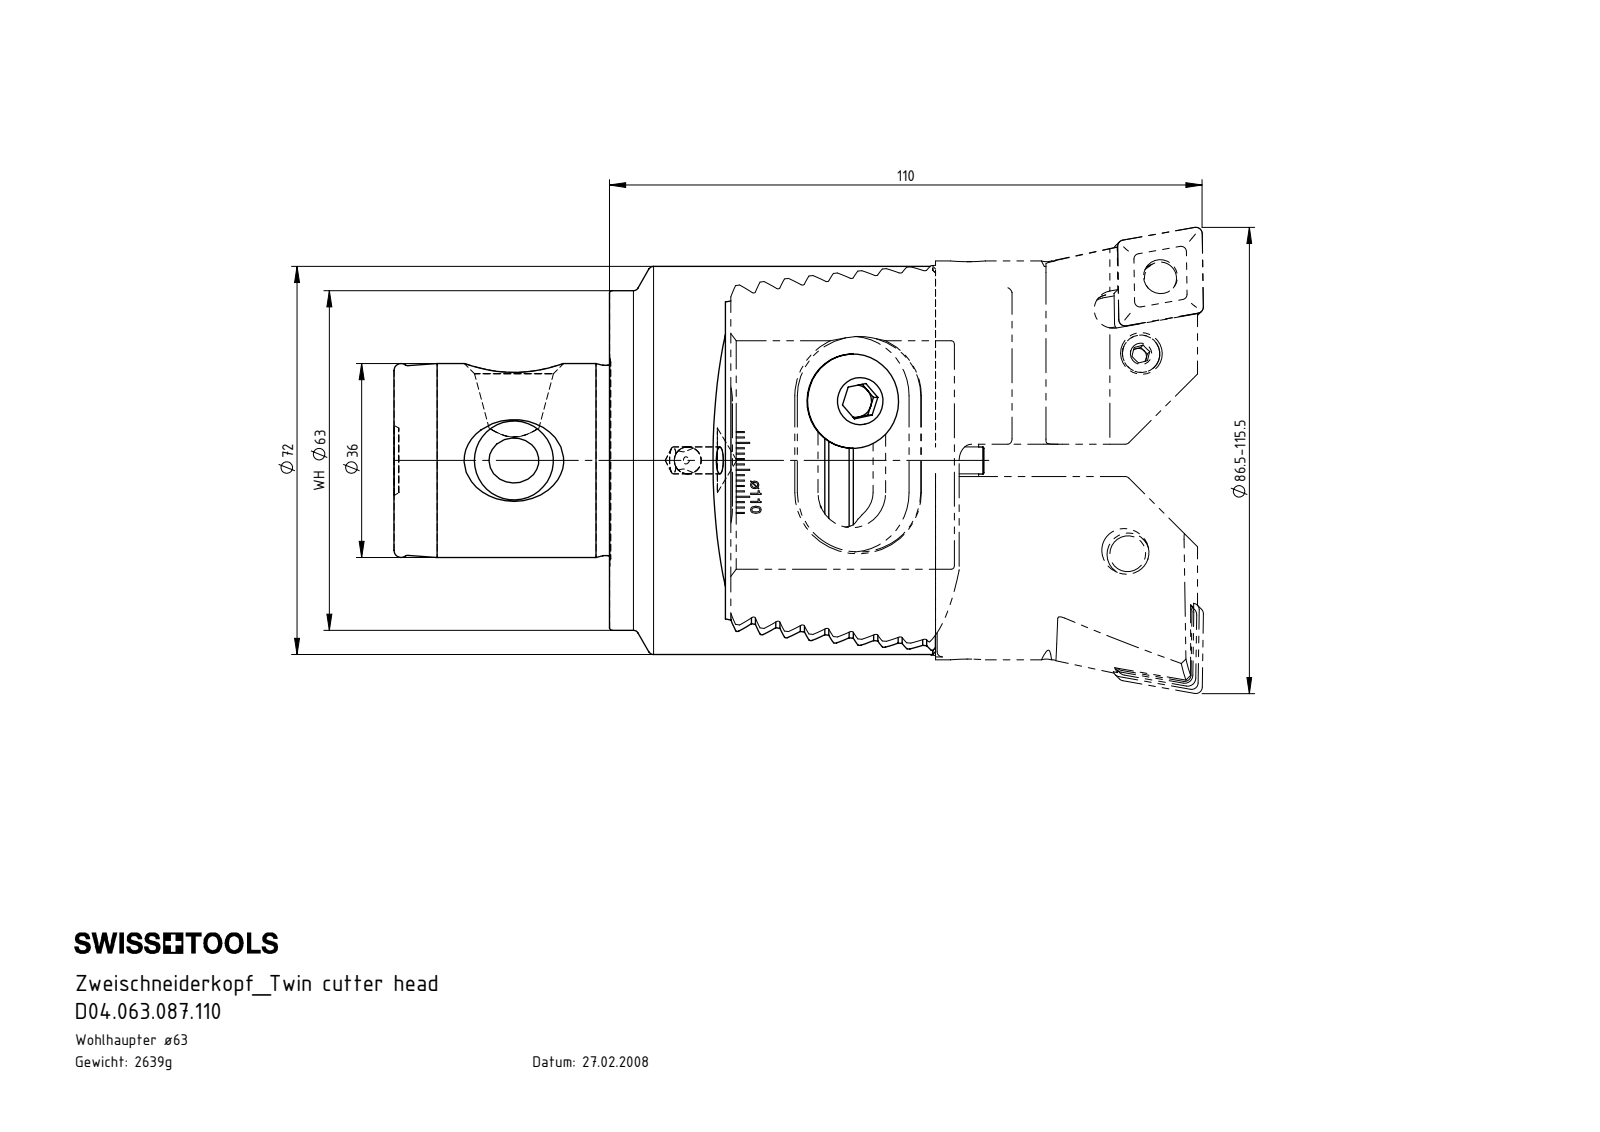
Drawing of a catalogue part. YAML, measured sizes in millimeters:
part_name: "Z42-ER2.001.019_A; Z55-ER1.001.025; CNMG160612; Z72-ER3.001.030 (+8 more)"
step_written_by: "SolidWorks 2015 (AUTOMOTIVE_DESIGN)"
units: millimeters
bodies: {solids: 20, faces: 1237, planar: 637, cylindrical: 268, other: 332}
overall_size: [150.22, 86, 72]
volume: 336168
surface_area: 79192
round_holes:
  - {diameter: 4.2, count: 3}
  - {diameter: 2, count: 2}
  - {diameter: 6.35, count: 2}
  - {diameter: 7, count: 2}
  - {diameter: 8.05, count: 2}
  - {diameter: 8.4, count: 2}
  - {diameter: 10.25, count: 2}
  - {diameter: 10.5, count: 2}
  - {diameter: 13.5, count: 2}
  - {diameter: 3.3, count: 1}
  - {diameter: 5, count: 1}
  - {diameter: 12, count: 1}
round_bosses_or_shafts:
  - {diameter: 6, count: 3}
  - {diameter: 17.5, count: 2}
  - {diameter: 17, count: 2}
  - {diameter: 10, count: 2}
  - {diameter: 8, count: 2}
  - {diameter: 7.9, count: 2}
  - {diameter: 6.4, count: 2}
  - {diameter: 4, count: 2}
partial_cylinders:
  - {radius: 0.34, count: 18}
  - {radius: 0.34, count: 16}
  - {radius: 1, count: 16}
  - {radius: 1.2, count: 8}
  - {radius: 1.5, count: 8}
  - {radius: 3, count: 6}
  - {radius: 3.5, count: 6}
  - {radius: 0.3, count: 4}
face_to_face_distances: [4.07, 8.14, 12.21, 24.43, 20.36, 4.11, 4.13, 4.03, 16.29, 8.2]
hole_center_spacings: [14.76, 15, 20, 38.64]
